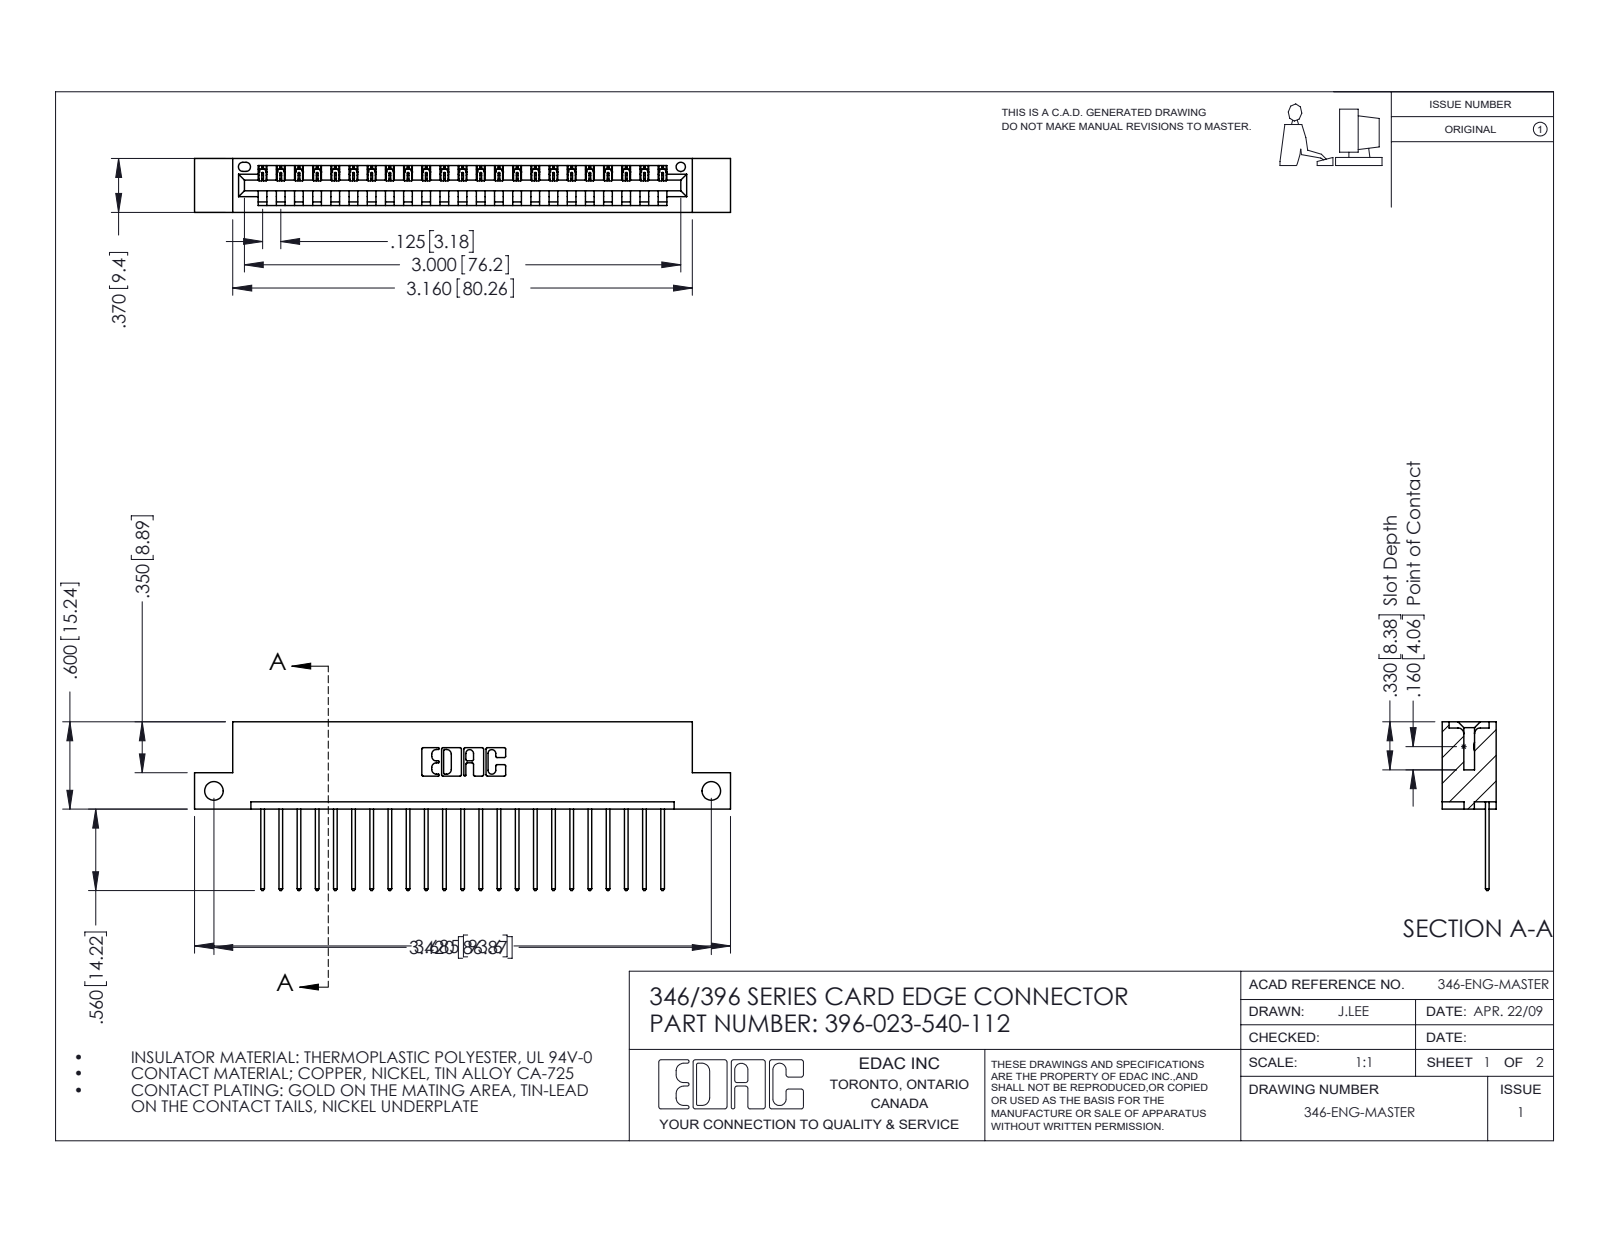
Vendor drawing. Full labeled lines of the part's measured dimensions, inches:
Part name (STEP PRODUCT): 396-023-540-112; 345-292-001_345-293-140; 346 Part_Flush Mounting Lugs - Side Mount
STEP written by: SolidWorks 2016 (CONFIG_CONTROL_DESIGN)
Units: inches
Bodies: 24 solids, 1456 faces (996 planar, 460 cylindrical, 0 other)
Overall size (bounding box): 3.685 × 1.16 × 0.37
Volume: 0.535 in³ · Surface area: 16.8 in²
Round holes (diameter × count): ⌀0.128 ×2, ⌀0.064 ×1
Partial cylindrical surfaces — rounded edges, fillets, slot ends (radius × count): R0.006 ×46, R0.01 ×46, R0.01 ×22, R0.007 ×6, R0.031 ×6, R0.026 ×3, R0.031 ×2, R0.04 ×2
Main face-to-face distances: 0.048, 0.322, 0.25, 0.37, 0.072, 0.298, 0.025, 0.148, 0.222, 0.1
Hole centre spacings: 3.42
